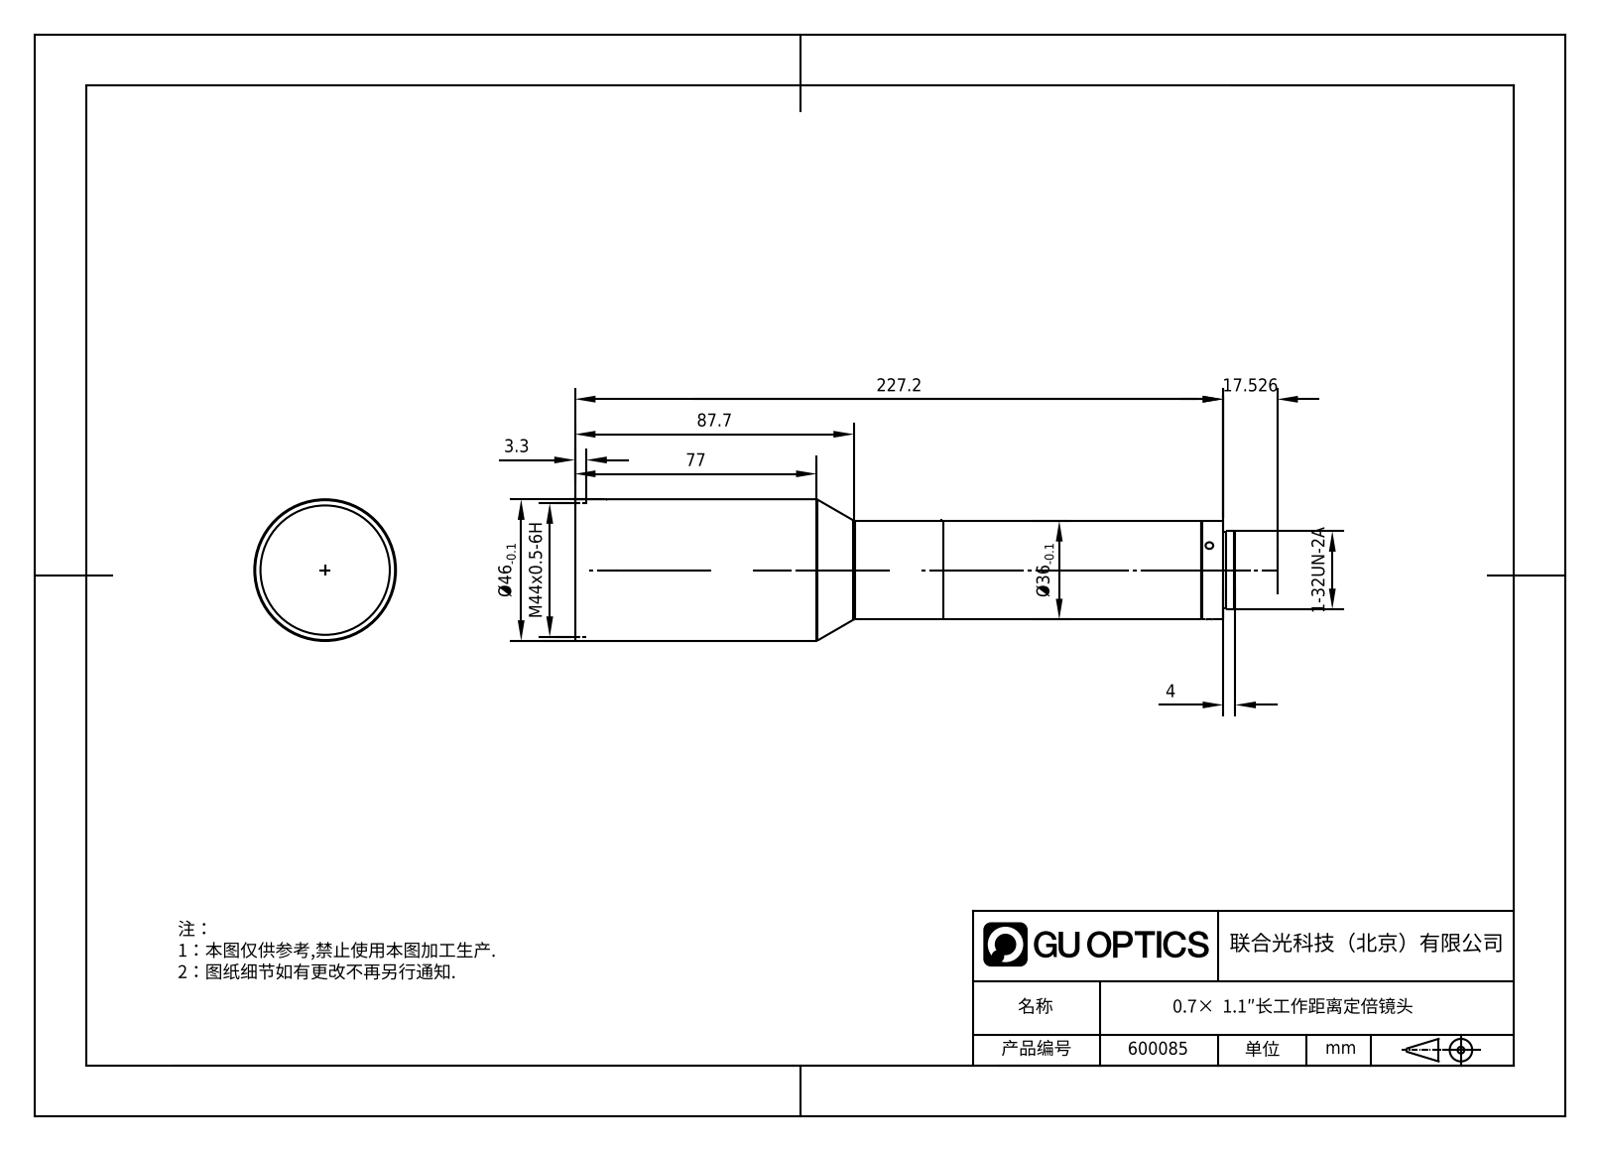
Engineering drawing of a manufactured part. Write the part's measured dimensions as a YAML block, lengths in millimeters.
part_name: "600085"
step_written_by: "SolidWorks 2020 (CONFIG_CONTROL_DESIGN)"
units: millimeters
bodies: {solids: 2, faces: 28, planar: 7, cylindrical: 12, other: 9}
overall_size: [231.16, 46, 46]
volume: 280111
surface_area: 35774
round_holes:
  - {diameter: 2.5, count: 3}
  - {diameter: 42, count: 1}
round_bosses_or_shafts:
  - {diameter: 46, count: 1}
  - {diameter: 36, count: 1}
  - {diameter: 25.4, count: 1}
  - {diameter: 24.6, count: 1}
partial_cylinders:
  - {radius: 17.2, count: 1}
face_to_face_distances: [218.16, 4, 222.16, 231.16, 227.16, 9, 3.2, 0.8, 218.96, 227.96]
